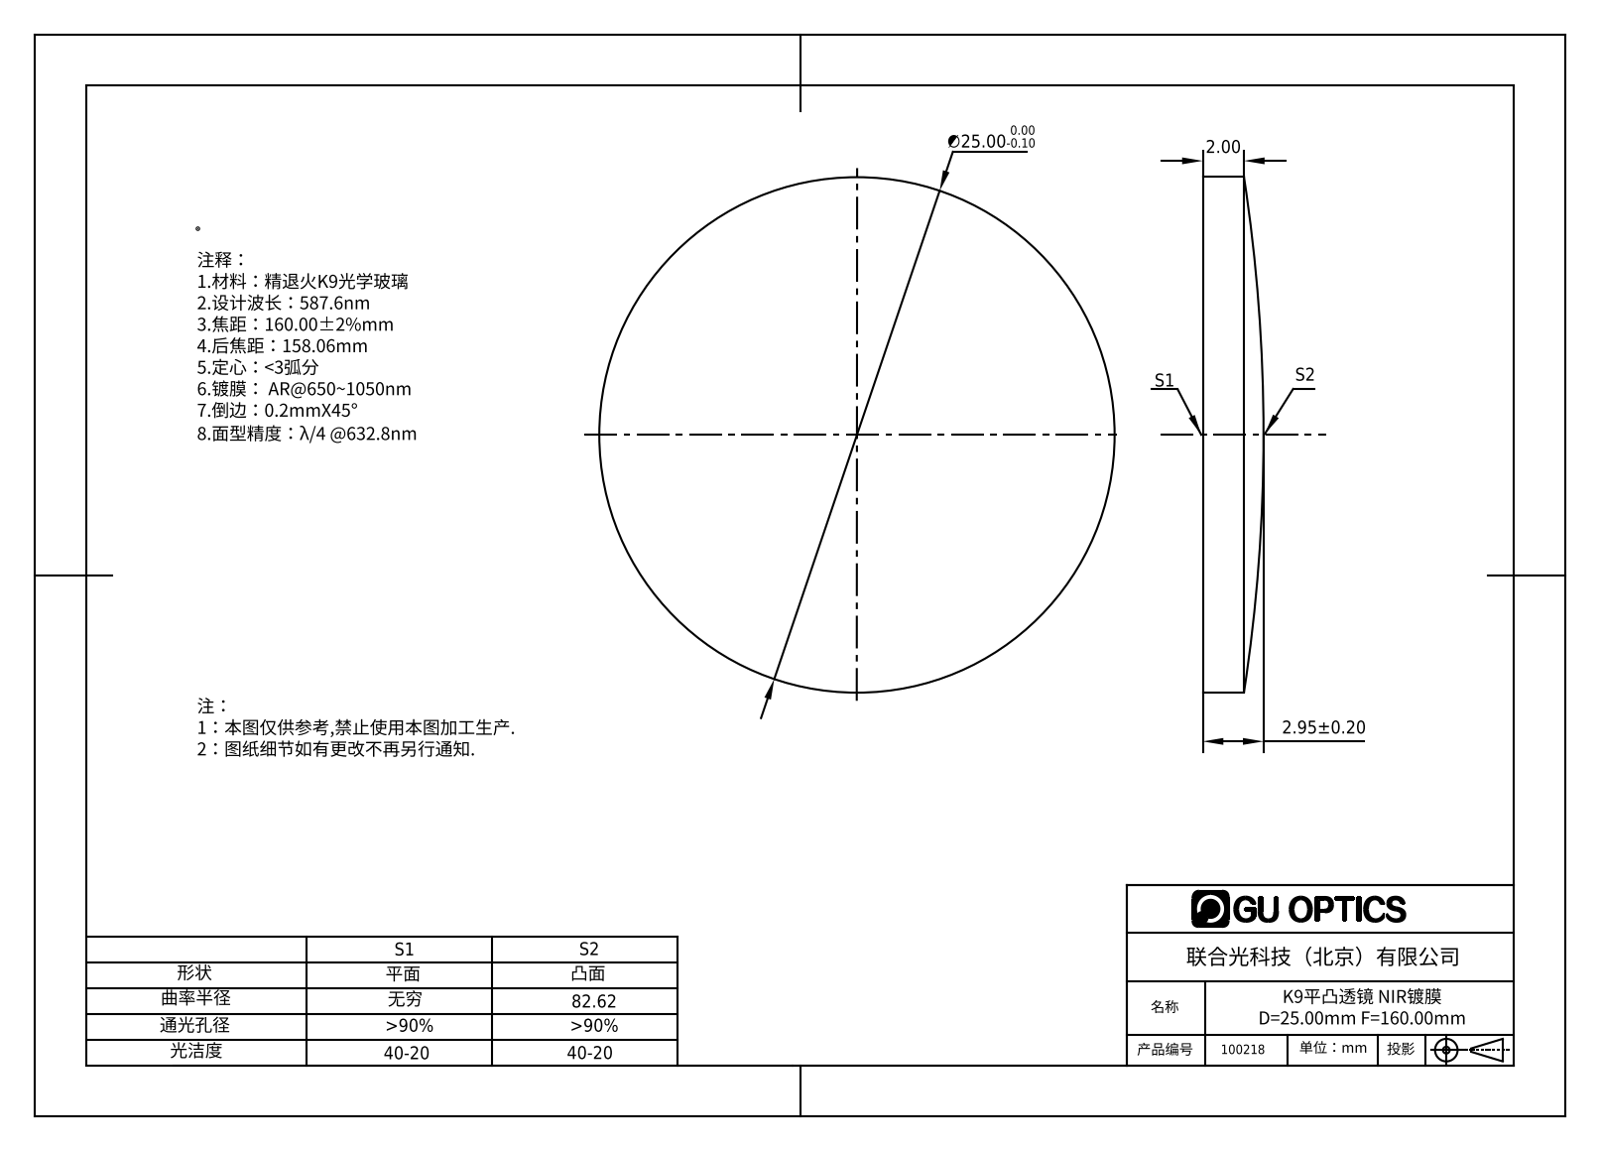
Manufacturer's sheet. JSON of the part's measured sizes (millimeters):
{"part_name": "100218", "step_written_by": "SolidWorks 2016 (AUTOMOTIVE_DESIGN)", "units": "millimeters", "bodies": {"solids": 1, "faces": 5, "planar": 1, "cylindrical": 2, "other": 2}, "overall_size": [25, 25, 2.95], "volume_mm3": 1215, "surface_area_mm2": 1142, "round_bosses_or_shafts": [[25, 1]]}
